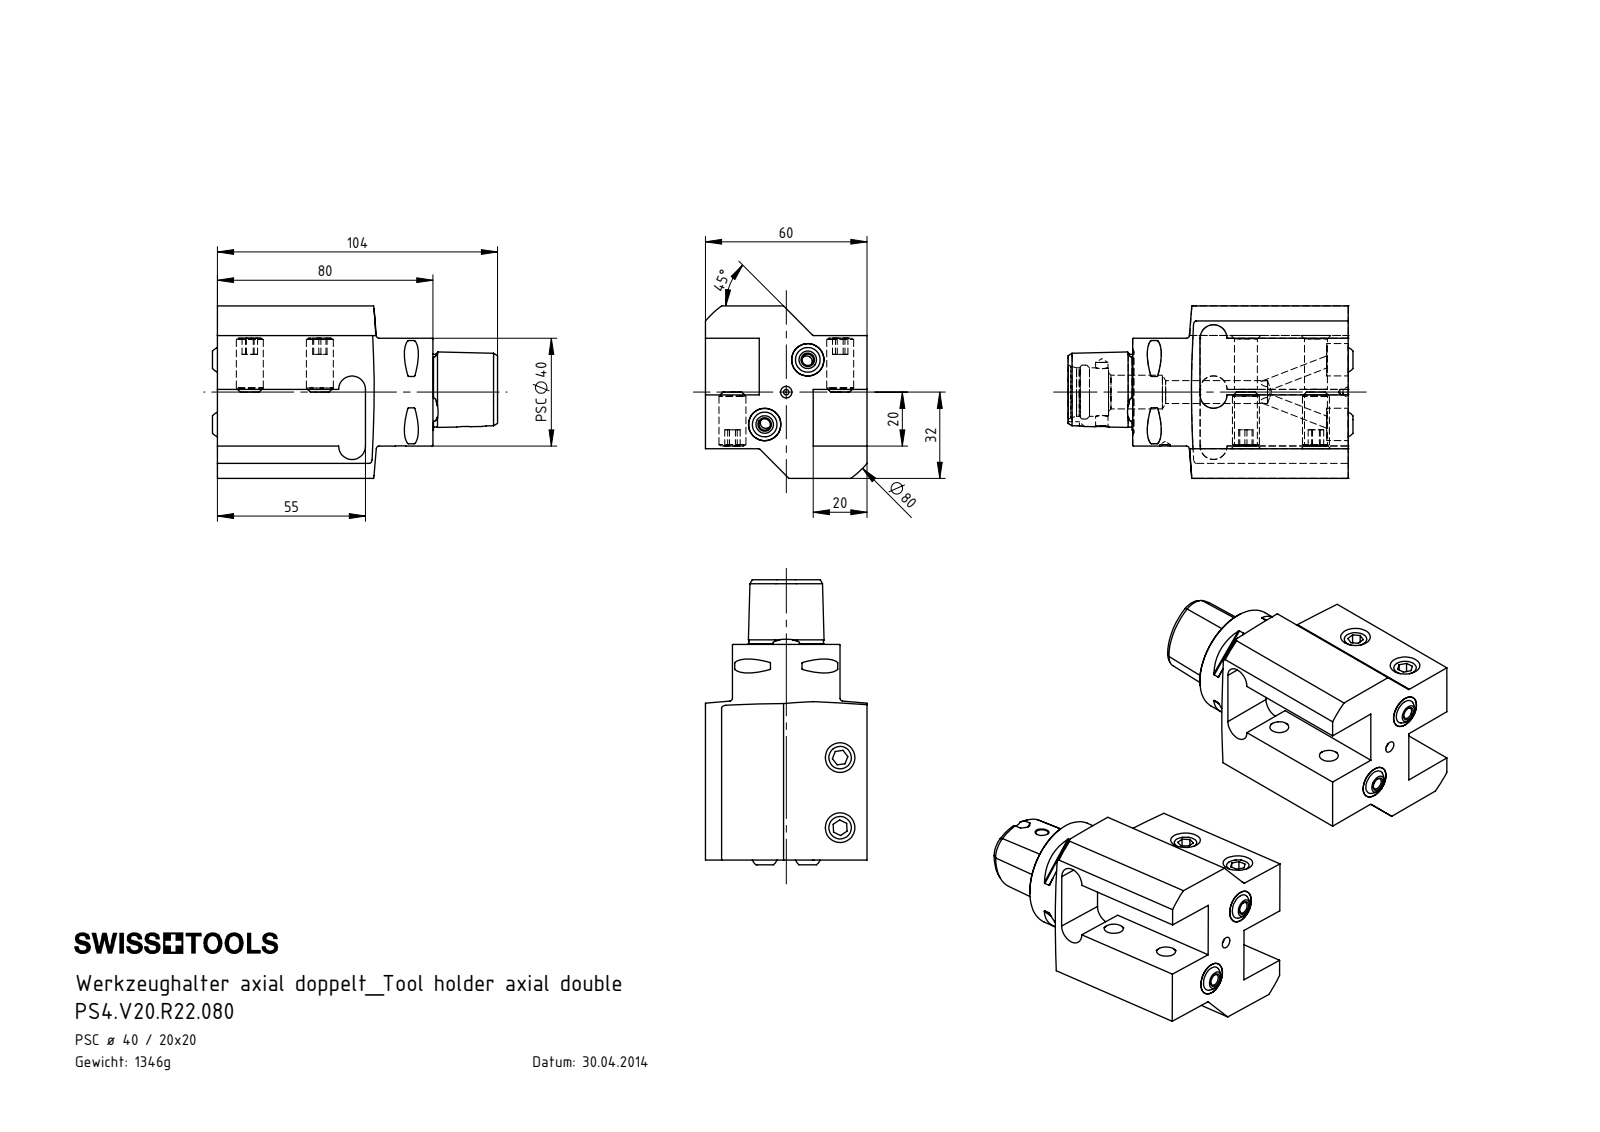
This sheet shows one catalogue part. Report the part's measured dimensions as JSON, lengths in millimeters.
{"part_name": "KU1-U12.001.010; ISO 4026 - M10 x 20_PreviewCfg; KU1-U12.001.010_2; PS4-V20.R22.080_A (+2 more)", "step_written_by": "SolidWorks 2017 (CONFIG_CONTROL_DESIGN)", "units": "millimeters", "bodies": {"solids": 9, "faces": 286, "planar": 79, "cylindrical": 75, "other": 132}, "overall_size": [105.8, 64, 60], "volume_mm3": 172115, "surface_area_mm2": 40255, "round_holes": [[8.5, 5], [4.2, 4], [7, 2], [12, 2], [2, 1], [4, 1], [4.6, 1], [12.5, 1], [18, 1], [20, 1]], "round_bosses_or_shafts": [[10, 4], [40, 1]], "partial_cylinders_radius": [[0.3, 8], [5, 4], [0.8, 2], [3, 1], [40, 1]], "face_to_face_distances": [20, 40, 1, 12, 52, 11, 53, 41, 21, 31], "hole_center_spacings": [14.42, 26, 36.06, 40, 47.71, 57.12, 59.46, 81.98]}
